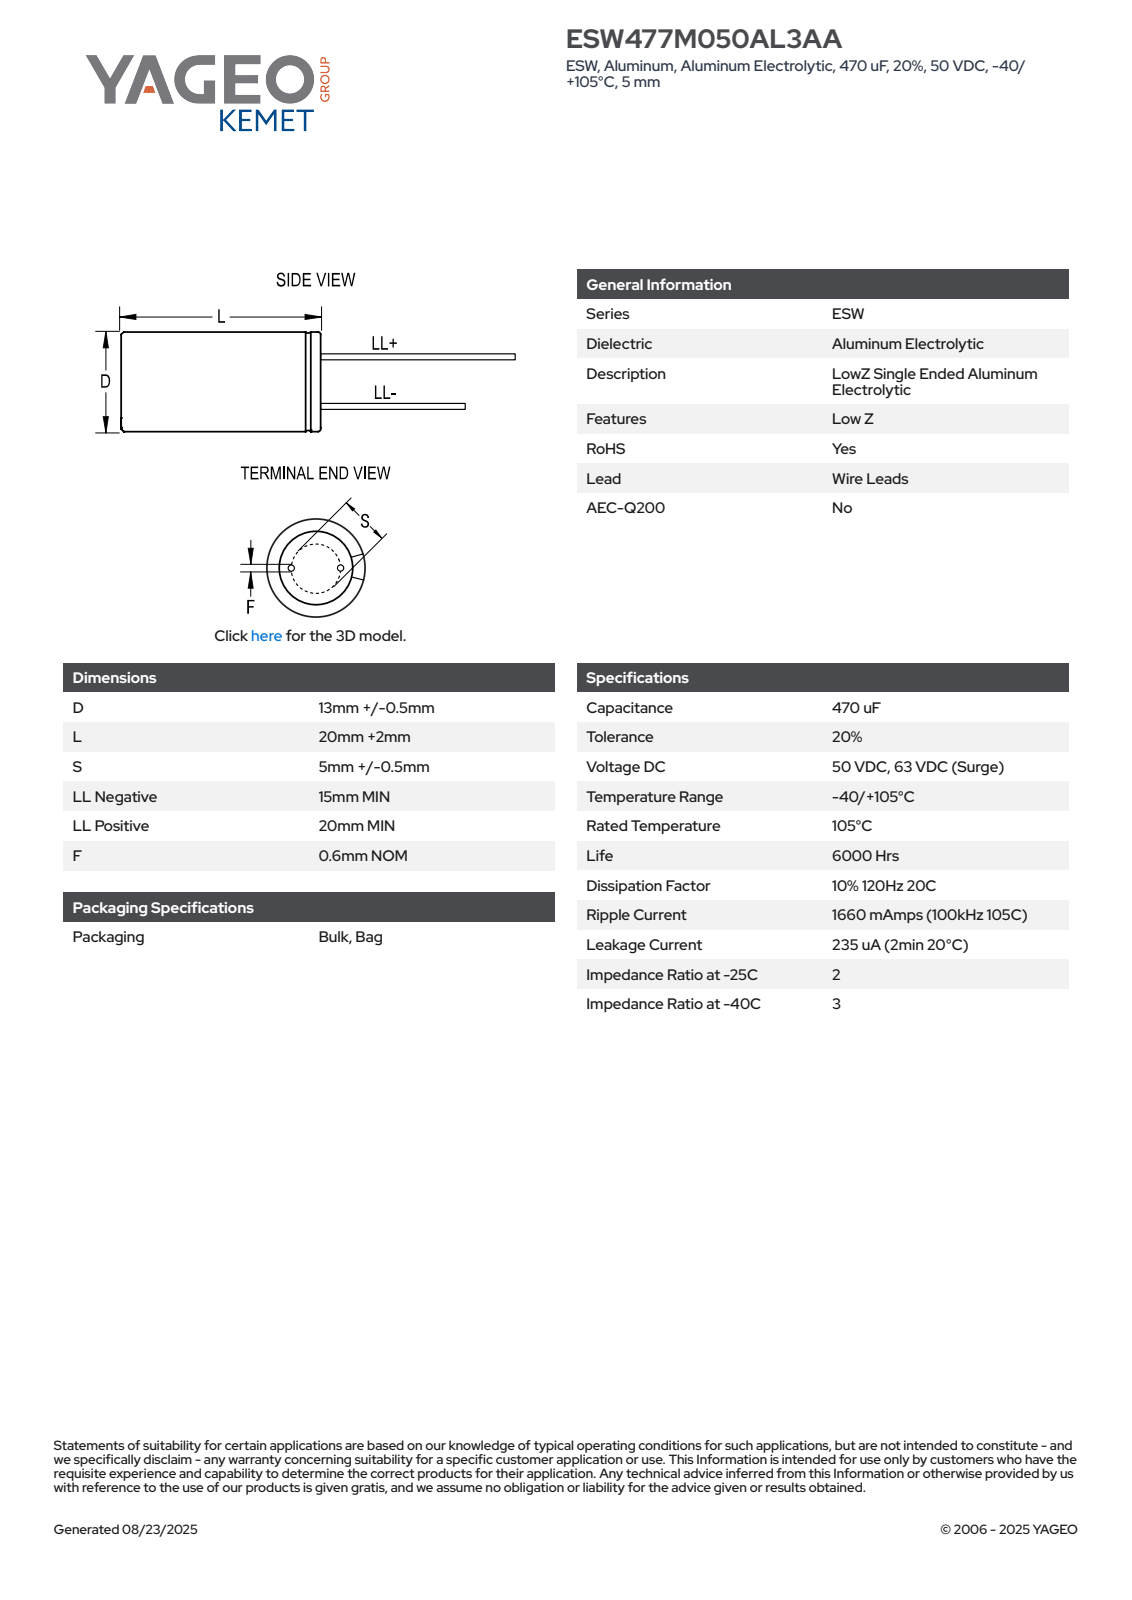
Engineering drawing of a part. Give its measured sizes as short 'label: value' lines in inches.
name: CAR_KLP_13X20_D13.5L22S5F0.6
written by: SolidWorks 2014 (AUTOMOTIVE_DESIGN)
unit: in
bodies: 4 solids, 75 faces (61 planar, 8 cylindrical, 6 other)
size: 1.654 × 0.531 × 0.531
volume: 0.191 in³; area: 2.057 in²
bosses: 2× ⌀0.024, 1× ⌀0.531
face distances: 0.866, 0.867, 1.457, 1.654, 1.457, 1.654, 0.591, 0.787, 0.197, 0.071
